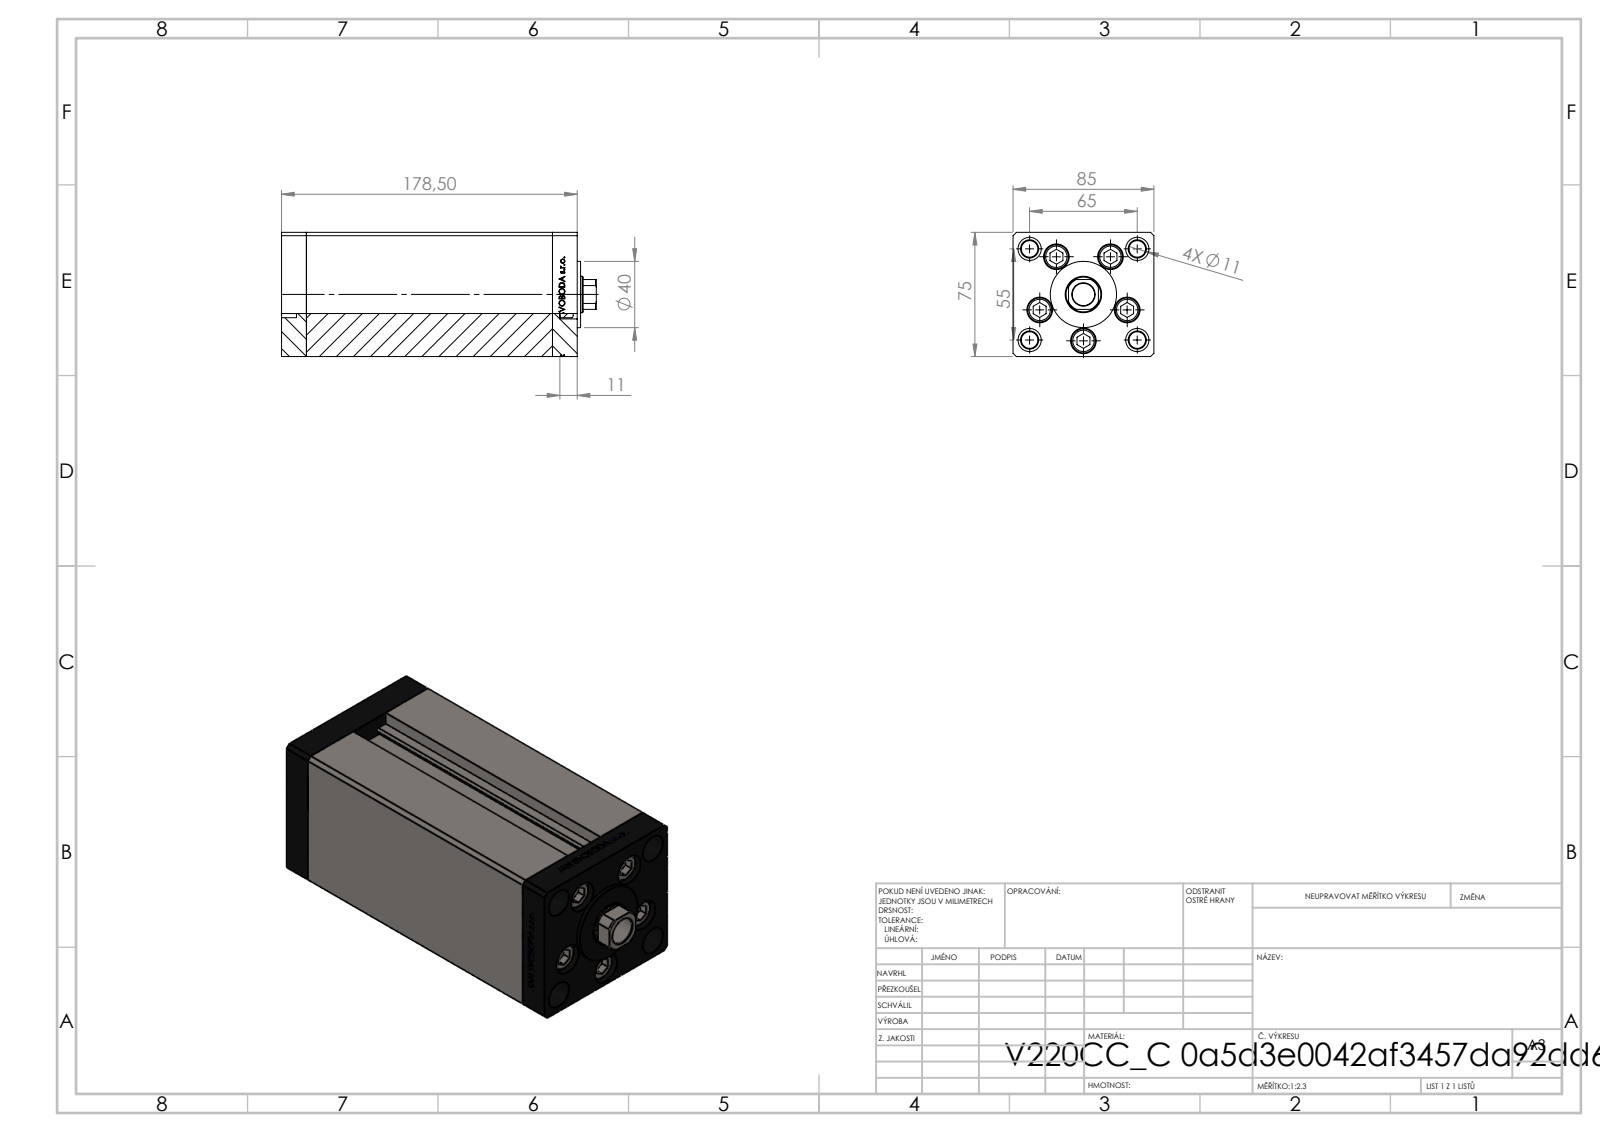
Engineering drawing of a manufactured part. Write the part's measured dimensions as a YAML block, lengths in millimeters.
part_name: "V220C_C MIDDLE; V220C FRONT; ALLEN BOLT; V220C BACK_C (+1 more)"
step_written_by: "SolidWorks 2019 (CONFIG_CONTROL_DESIGN)"
units: millimeters
bodies: {solids: 13, faces: 1159, planar: 538, cylindrical: 159, other: 462}
overall_size: [190, 85, 75]
volume: 949001
surface_area: 179253
round_holes:
  - {diameter: 11, count: 9}
  - {diameter: 15.5, count: 5}
  - {diameter: 10, count: 4}
  - {diameter: 14, count: 4}
  - {diameter: 13.5, count: 1}
  - {diameter: 14.5, count: 1}
  - {diameter: 22, count: 1}
round_bosses_or_shafts:
  - {diameter: 8, count: 5}
  - {diameter: 14.5, count: 4}
  - {diameter: 40, count: 1}
partial_cylinders:
  - {radius: 0.93, count: 2}
  - {radius: 10.5, count: 1}
face_to_face_distances: [85, 75, 15, 148.5, 163.5, 10.5, 178.5, 34.25, 144.25, 129.25]
hole_center_spacings: [28, 42.57, 16.86, 19.17, 32.33, 32.5, 33.63, 37.33]
